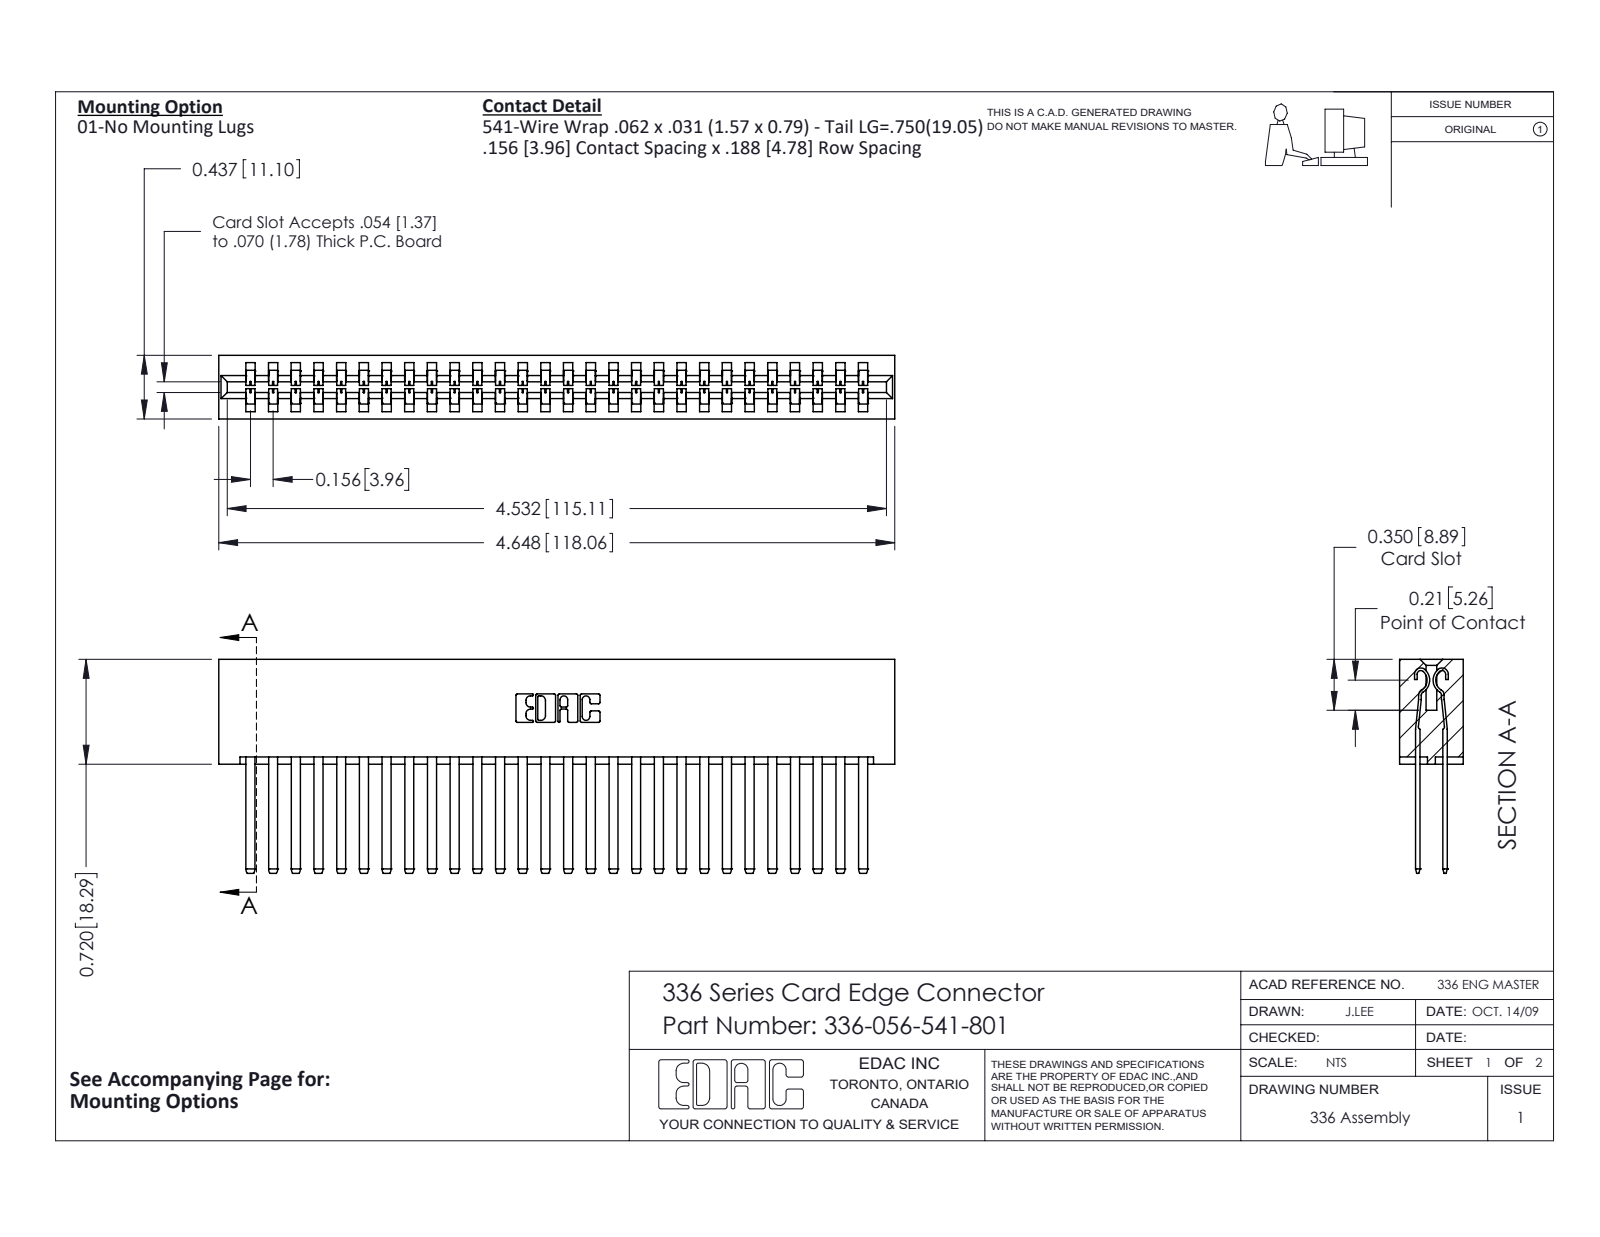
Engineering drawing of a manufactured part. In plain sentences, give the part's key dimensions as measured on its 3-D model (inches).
The part is named "336 Part_Lugless; 336-056-541-801; 336-290-001_336-290-541". Its 3-D file was written by "SolidWorks 2020 (CONFIG_CONTROL_DESIGN)". It is 57 solids with 2458 faces: 1522 planar, 936 cylindrical and 0 other. Overall it measures 4.648 by 1.47 by 0.437 inches. Its volume is 1.188 cubic inches and its surface area 38.48 square inches. Partial cylindrical surfaces (rounded edges, fillets, slot ends): 112 of radius 0.004, 56 of radius 0.056, 22 of radius 0.01, 6 of radius 0.007, 6 of radius 0.031, 4 of radius 0.022, 4 of radius 0.04, 3 of radius 0.026. The main face-to-face distances are 0.188, 0.328, 0.14, 0.297, 0.109, 0.031, 0.437, 0.033, 0.181, 0.256.
